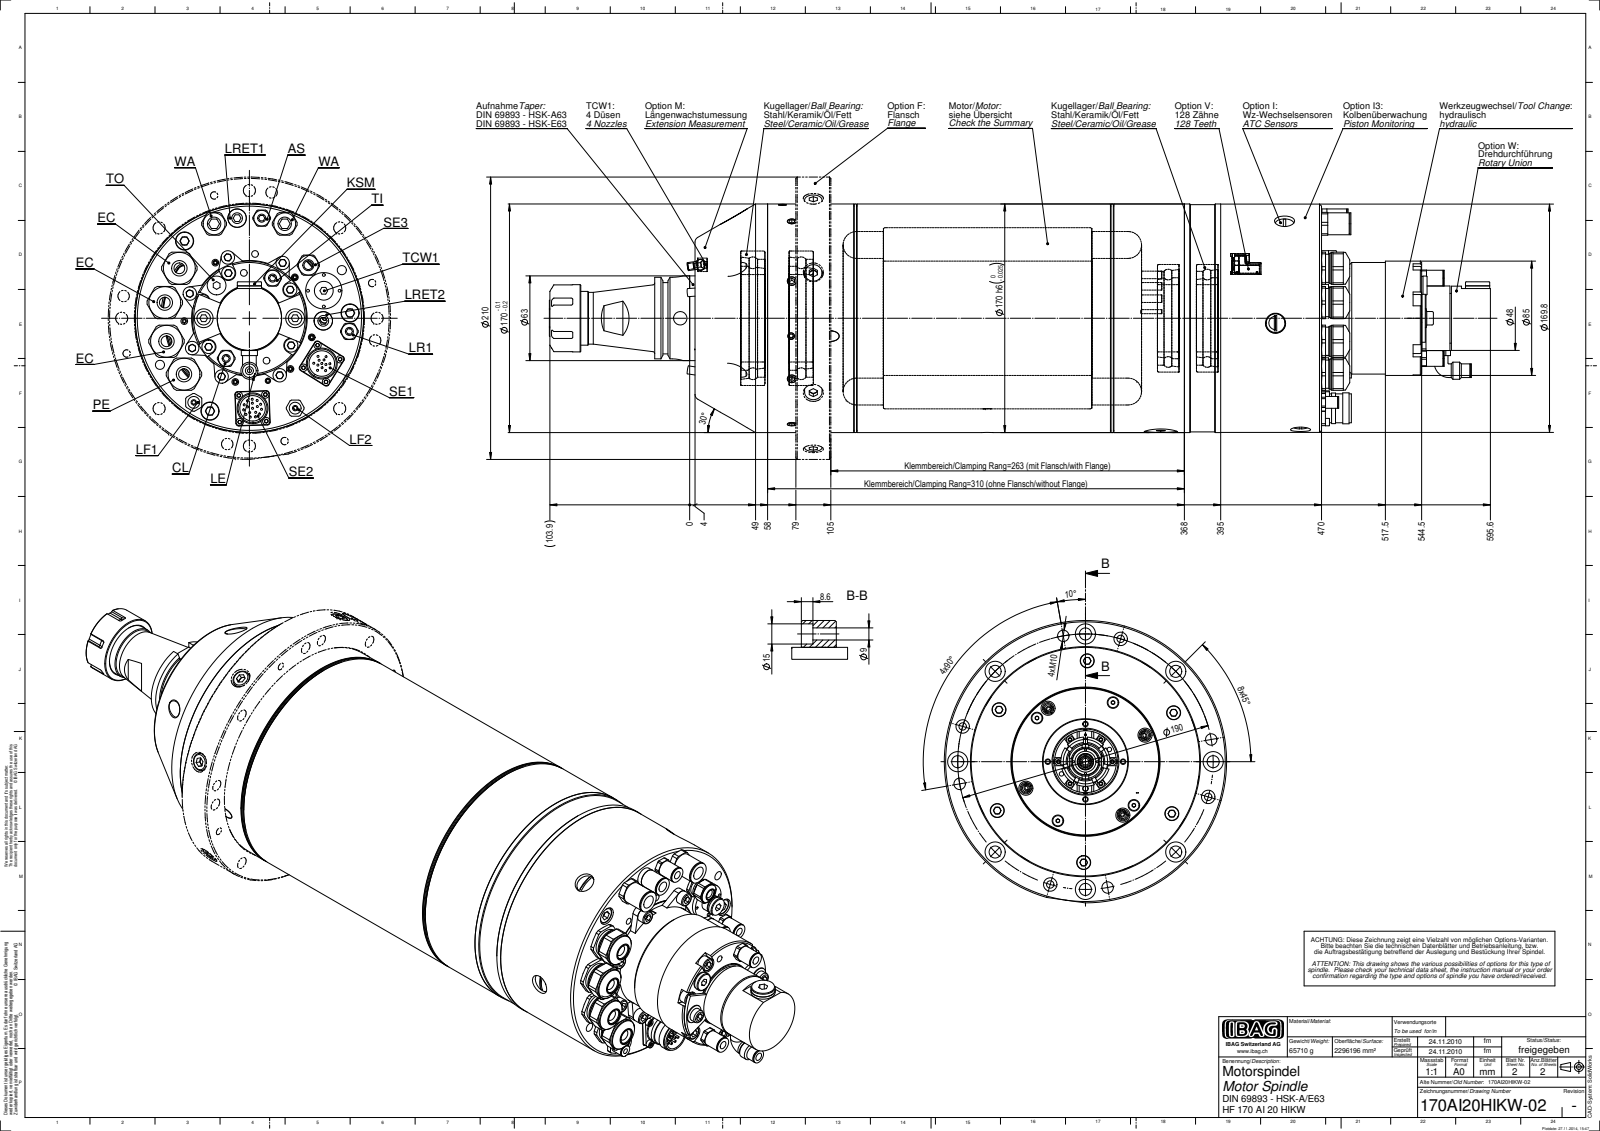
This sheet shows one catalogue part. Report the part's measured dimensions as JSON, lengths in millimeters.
{"part_name": "170AI20HIKW-02", "step_written_by": "SolidWorks 2010 (CONFIG_CONTROL_DESIGN)", "units": "millimeters", "bodies": {"solids": 0, "faces": 1371, "planar": 561, "cylindrical": 565, "other": 245}, "overall_size": [694.64, 170, 170], "round_holes": [[5, 8], [15, 7], [8, 6], [10.4, 6], [6, 5], [2.1, 4], [4.5, 4], [10, 4], [11.5, 4], [13.5, 3], [3.3, 2], [4, 2]], "round_bosses_or_shafts": [[1.5, 29], [10, 14], [5.5, 8], [14, 5], [23.7, 4], [22.3, 4], [20.96, 4], [11.7, 4]], "partial_cylinders_radius": [[1, 12], [5.5, 6], [6.6, 6], [8, 4], [13.2, 4], [9.25, 2], [8.25, 1], [22.15, 1]], "face_to_face_distances": [337, 27, 412, 75, 310, 102, 54, 364, 391, 466], "hole_center_spacings": [75, 48.5, 64, 17.63, 23.44, 27.7, 31.71, 35.66]}
